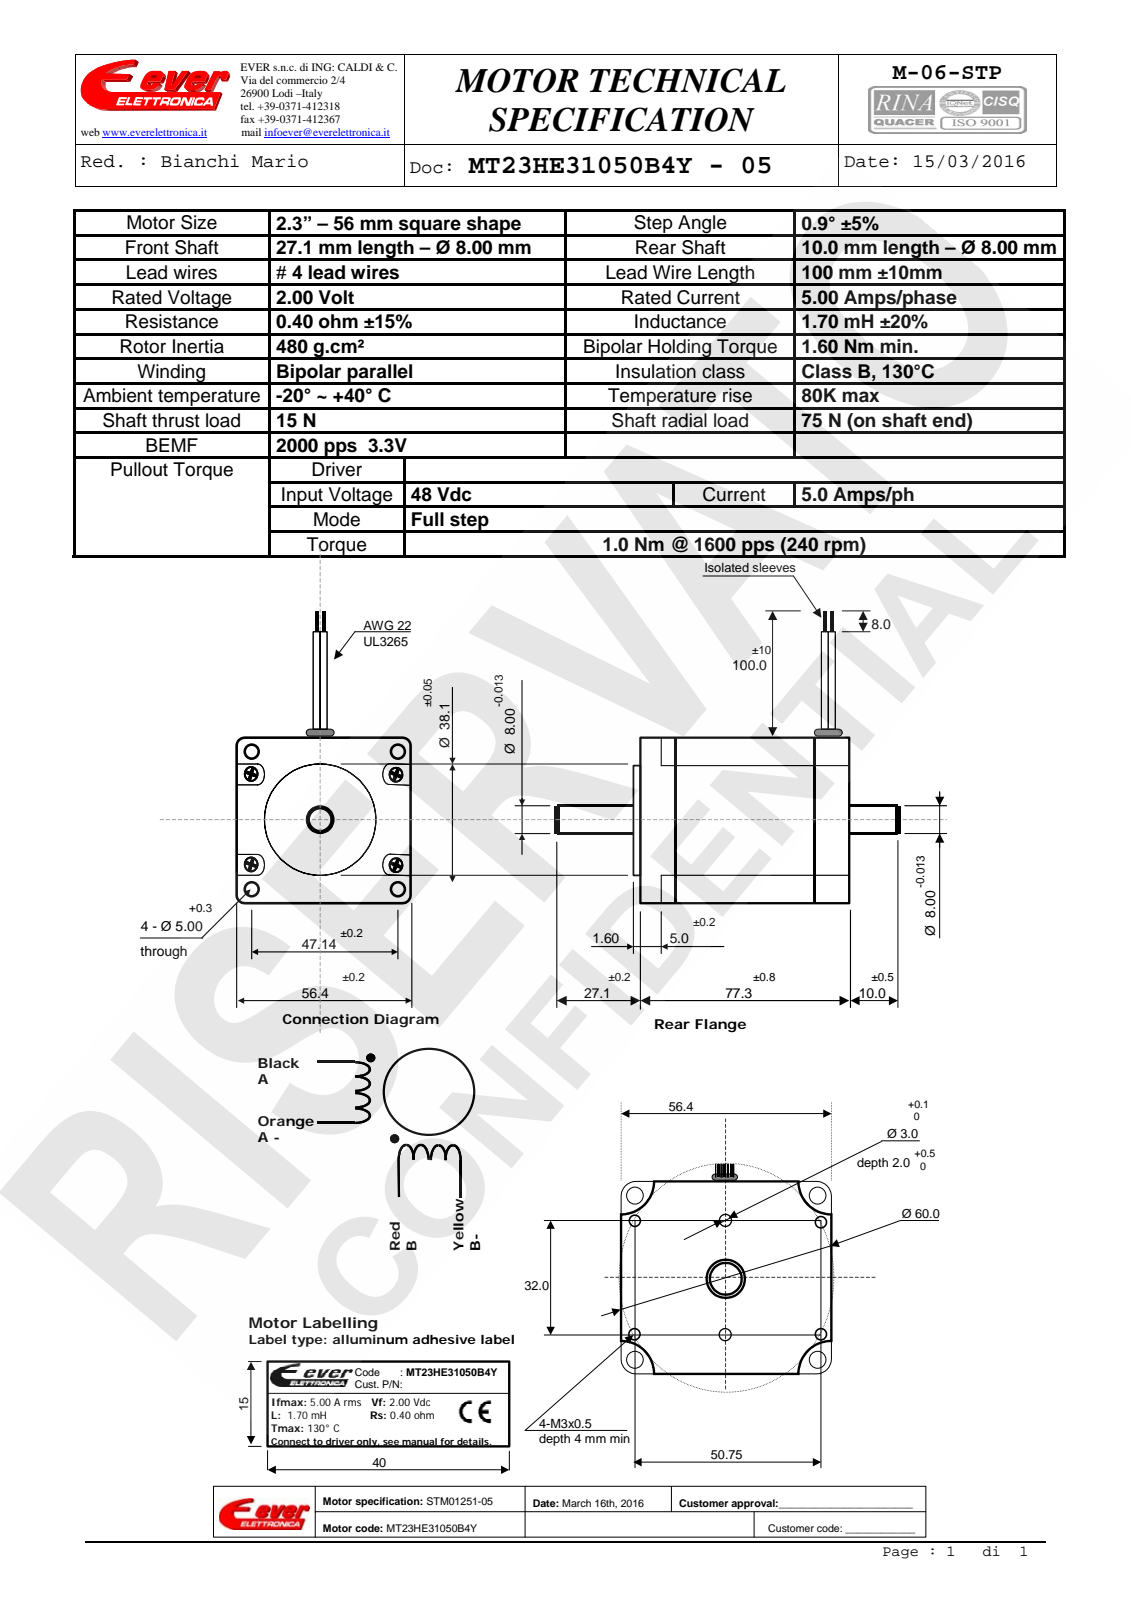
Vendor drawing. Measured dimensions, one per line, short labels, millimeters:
name: MT23HE_FLANGIA_FRONT_FOR5; MT23HE31_STACK; MT23HE_FLANGIA_POST_6_FORI_ENC; TCC_M3X25 (+4 more)
written by: PRO/ENGINEER BY PARAMETRIC TECHNOLOGY CORPORATION, 2006320 (AUTOMOTIVE_DESIGN_CC2)
unit: mm
bodies: 14 solids, 366 faces (150 planar, 142 cylindrical, 74 other)
size: 114.4 × 58.4 × 56.4
volume: 226 865 mm³; area: 41 858 mm²
holes: 6× ⌀3, 4× ⌀3.1, 4× ⌀3.2, 4× ⌀5, 1× ⌀6, 1× ⌀9.75, 1× ⌀10
bosses: 4× ⌀6, 4× ⌀3, 4× ⌀1, 1× ⌀38.1, 1× ⌀17, 1× ⌀8
rounds: 12× R3, 8× R0.5, 8× R0.75, 4× R5
face distances: 57.3, 56.4, 11.5, 68.8, 77.3, 65.8, 8.5, 1.6, 78.9, 67.4
hole spacings: 32, 0.38, 7.62, 7.7, 7.78, 24.76, 25, 25.38
